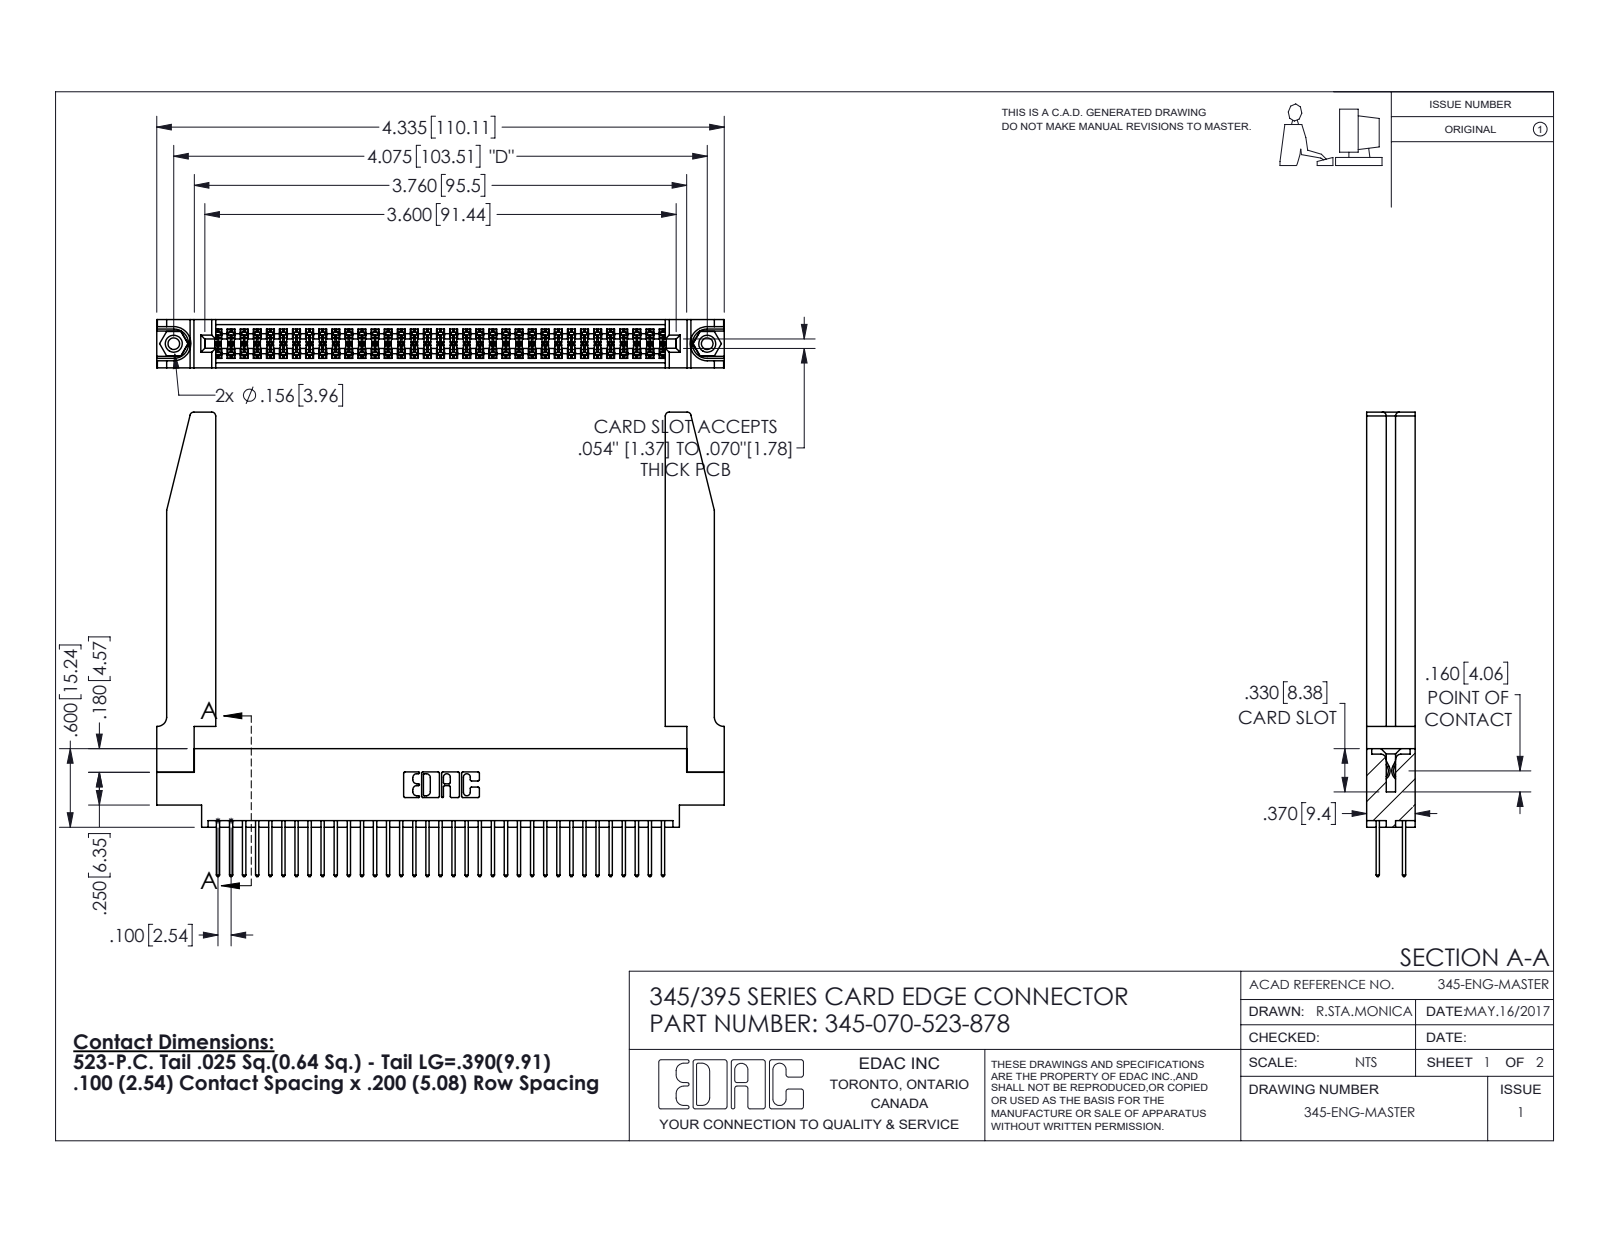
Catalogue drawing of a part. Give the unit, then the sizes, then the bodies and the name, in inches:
Units: inches
Overall size (bounding box): 4.336 × 3.547 × 0.37
Round holes (diameter × count): ⌀0.089 ×2, ⌀0.125 ×2, ⌀0.156 ×2, ⌀0.064 ×1
Round bosses / shafts (diameter × count): ⌀0.155 ×2
Partial cylindrical surfaces — rounded edges, fillets, slot ends (radius × count): R0.006 ×105, R0.01 ×70, R0.01 ×22, R0.03 ×8, R0.007 ×6, R0.031 ×6, R0.026 ×3, R0.014 ×2
Main face-to-face distances: 0.37, 0.072, 0.298, 0.098, 0.272, 0.025, 0.2, 0.225, 0.175, 0.148
Hole centre spacings: 0.27, 3.839, 4.075
Volume: 1.125 in³ · Surface area: 36.04 in²
Bodies: 75 solids, 3864 faces (2536 planar, 1276 cylindrical, 52 other)
Part name (STEP PRODUCT): 345-250-001_345-250-001-102; 345-292-001_345-293-123; 345-220-078_345-220-078; 345 Part_0.170 Offset - 0.156 Dia-TH (+1 more)
STEP written by: SolidWorks 2016 (CONFIG_CONTROL_DESIGN)
